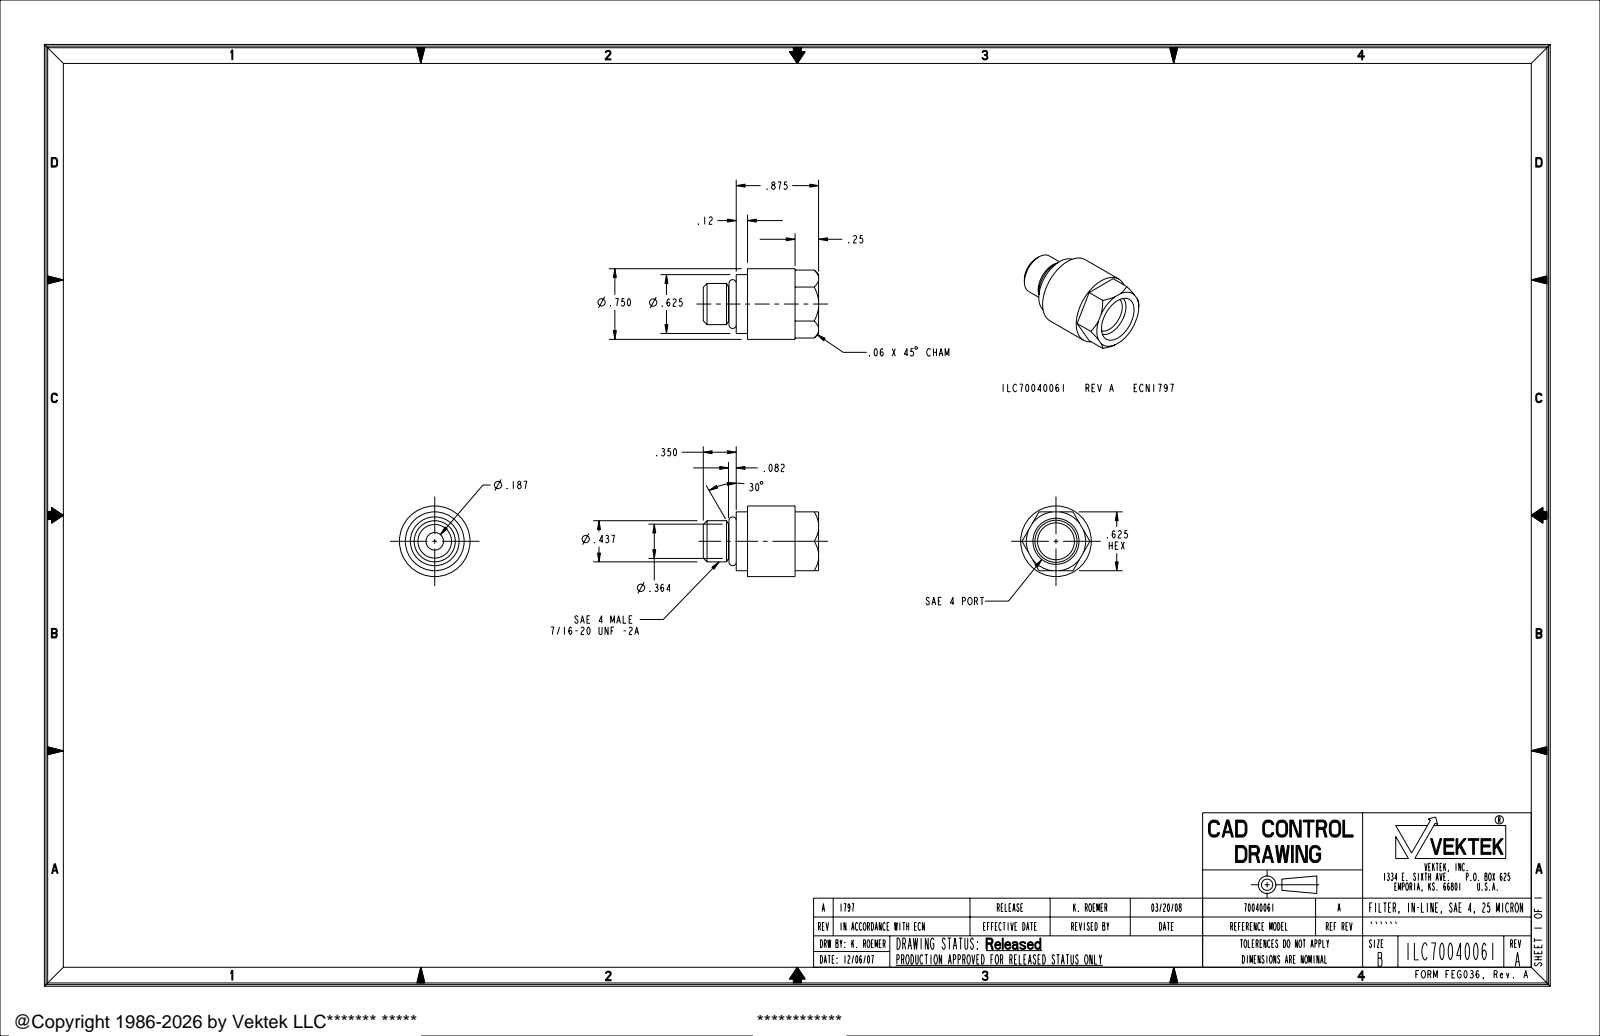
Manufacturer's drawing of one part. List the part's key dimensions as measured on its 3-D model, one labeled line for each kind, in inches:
Part name (STEP PRODUCT): ILC70040061
STEP written by: PRO/ENGINEER BY PARAMETRIC TECHNOLOGY CORPORATION, 2007460 (AUTOMOTIVE_DESIGN_CC2)
Units: inches
Bodies: 1 solid, 48 faces (14 planar, 14 cylindrical, 20 other)
Overall size (bounding box): 1.225 × 0.75 × 0.75
Volume: 0.321 in³ · Surface area: 4.417 in²
Round holes (diameter × count): ⌀0.187 ×1, ⌀0.392 ×1
Round bosses / shafts (diameter × count): ⌀0.75 ×1, ⌀0.625 ×1, ⌀0.437 ×1, ⌀0.364 ×1
Main face-to-face distances: 0.625, 0.12, 0.875, 0.755, 0.391, 0.271, 0.484, 0.625, 0.505, 0.234
